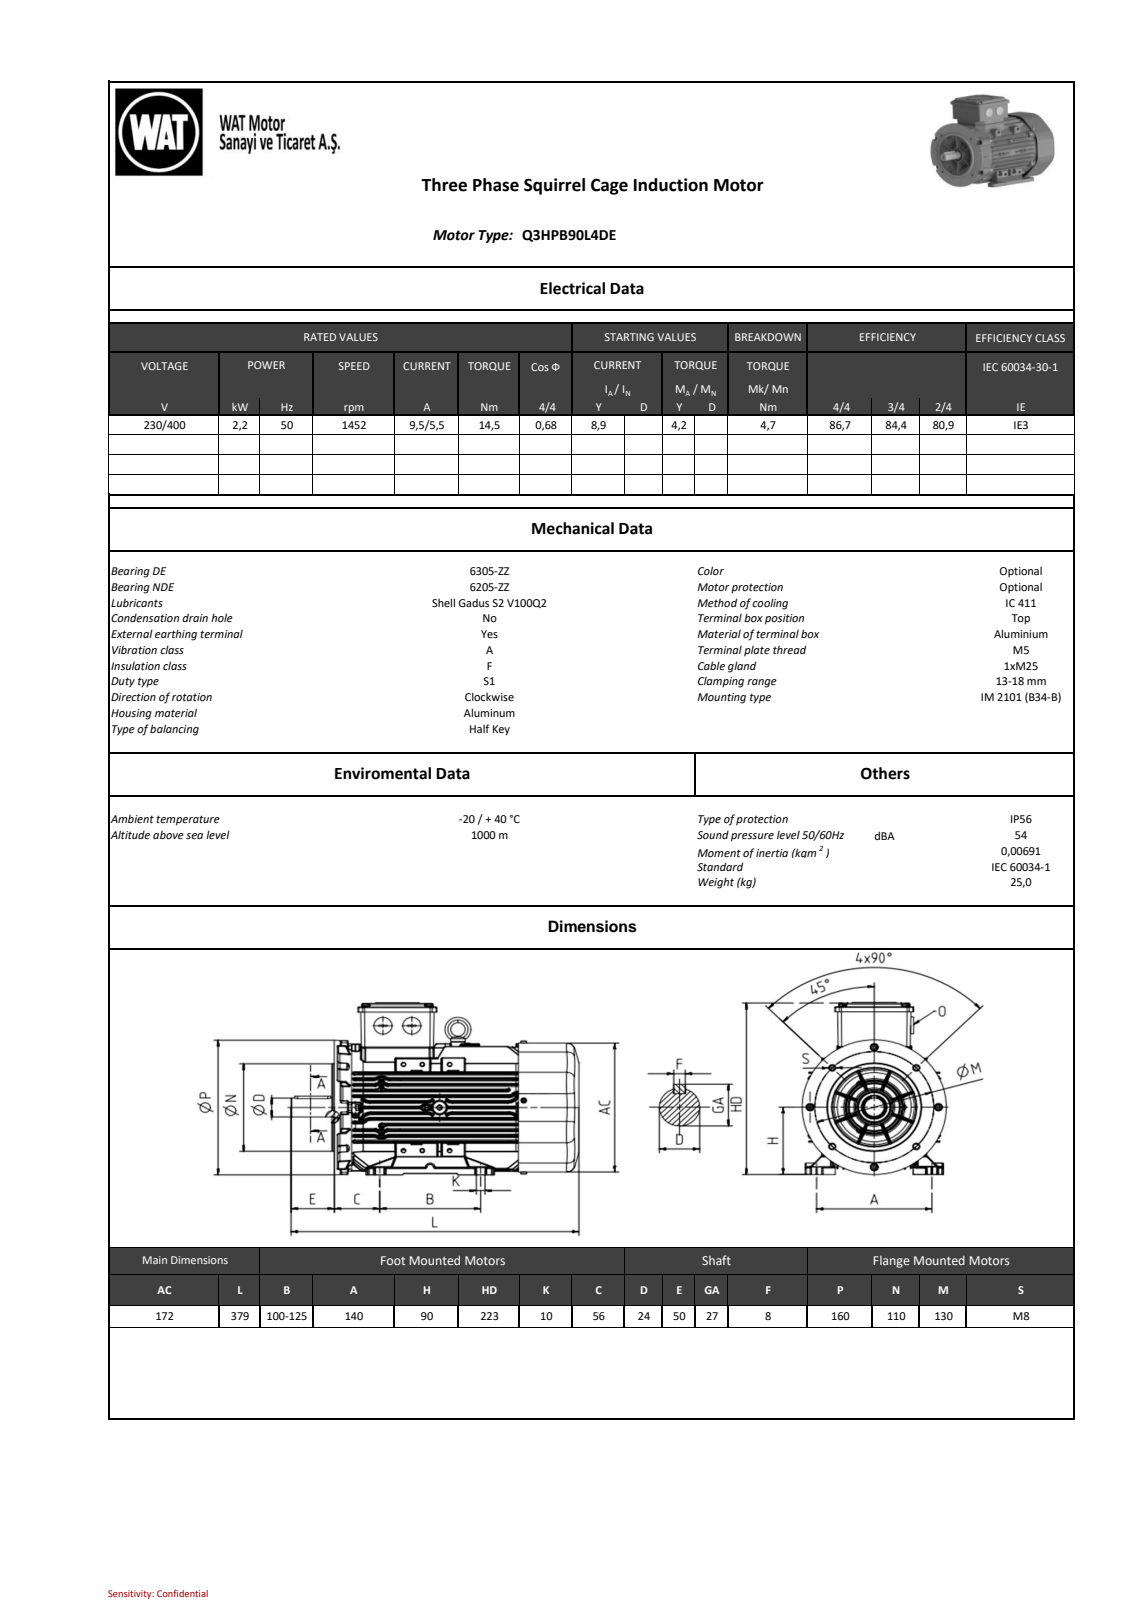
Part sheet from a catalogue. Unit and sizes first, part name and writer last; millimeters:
Units: millimetres
Overall size (bounding box): 378.54 × 223.05 × 172.19
Round holes (diameter × count): ⌀6.8 ×4, ⌀8.4 ×1, ⌀9.87 ×1, ⌀40 ×1, ⌀79.79 ×1, ⌀97.79 ×1, ⌀115.78 ×1
Round bosses / shafts (diameter × count): ⌀8 ×7, ⌀5 ×4, ⌀25 ×3, ⌀10 ×2, ⌀110 ×1, ⌀102.19 ×1, ⌀84.19 ×1, ⌀37.42 ×1
Partial cylindrical surfaces — rounded edges, fillets, slot ends (radius × count): R0.8 ×619, R1 ×515, R0.5 ×221, R2 ×65, R0.98 ×35, R8 ×28, R1.5 ×10, R4 ×10
Main face-to-face distances: 7.5, 91.91, 8.93, 82.98, 23.57, 50.35, 1.25, 7.37, 90.35, 16.87
Hole centre spacings: 65, 91.93, 64.97, 65.04, 130.01
Bodies: 0 solids, 6726 faces (1618 planar, 2338 cylindrical, 2770 other)
Part name (STEP PRODUCT): model2_objects
STEP written by: SIEMENS PLM Software NX2206.8101 (AUTOMOTIVE_DESIGN)
